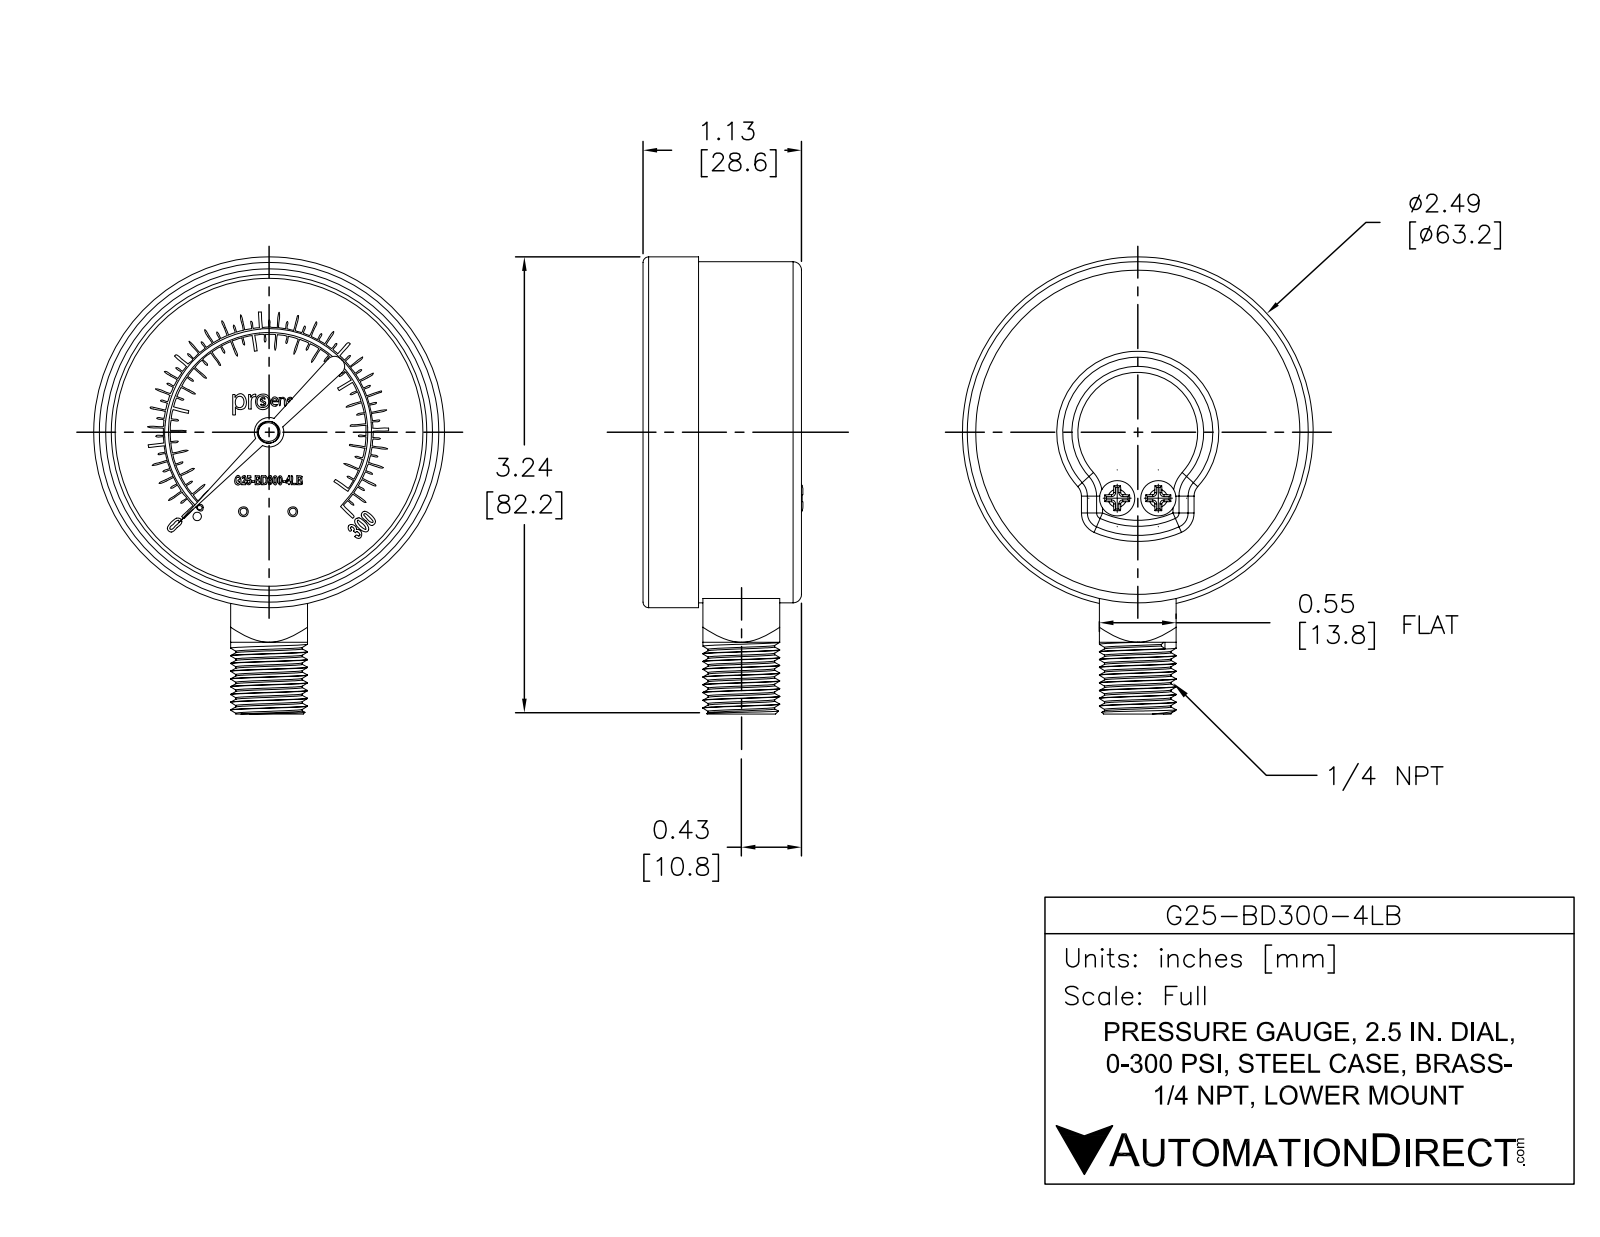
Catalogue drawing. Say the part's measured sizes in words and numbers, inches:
The part is named "G25-BD300-4LB". Its 3-D file was written by "SolidWorks 2021 (AUTOMOTIVE_DESIGN)". It is 1 solid with 225 faces: 112 planar, 35 cylindrical and 78 other. Overall it measures 3.245 by 2.49 by 1.135 inches. Its volume is 4.288 cubic inches and its surface area 22.39 square inches. Round holes: 1 of diameter 0.14, 1 of diameter 2.185. Round bosses or shafts: 2 of diameter 0.25, 1 of diameter 2.49, 1 of diameter 2.421, 1 of diameter 0.545, 1 of diameter 0.154, 1 of diameter 0.123, 1 of diameter 0.06. Partial cylindrical surfaces (rounded edges, fillets, slot ends): 6 of radius 0.06, 1 of radius 0.105, 1 of radius 0.803, 1 of radius 0.818. The main face-to-face distances are 0.835, 0.1, 0.735, 1.125, 1.025, 0.29, 0.545, 0.731, 0.631, 0.104.
